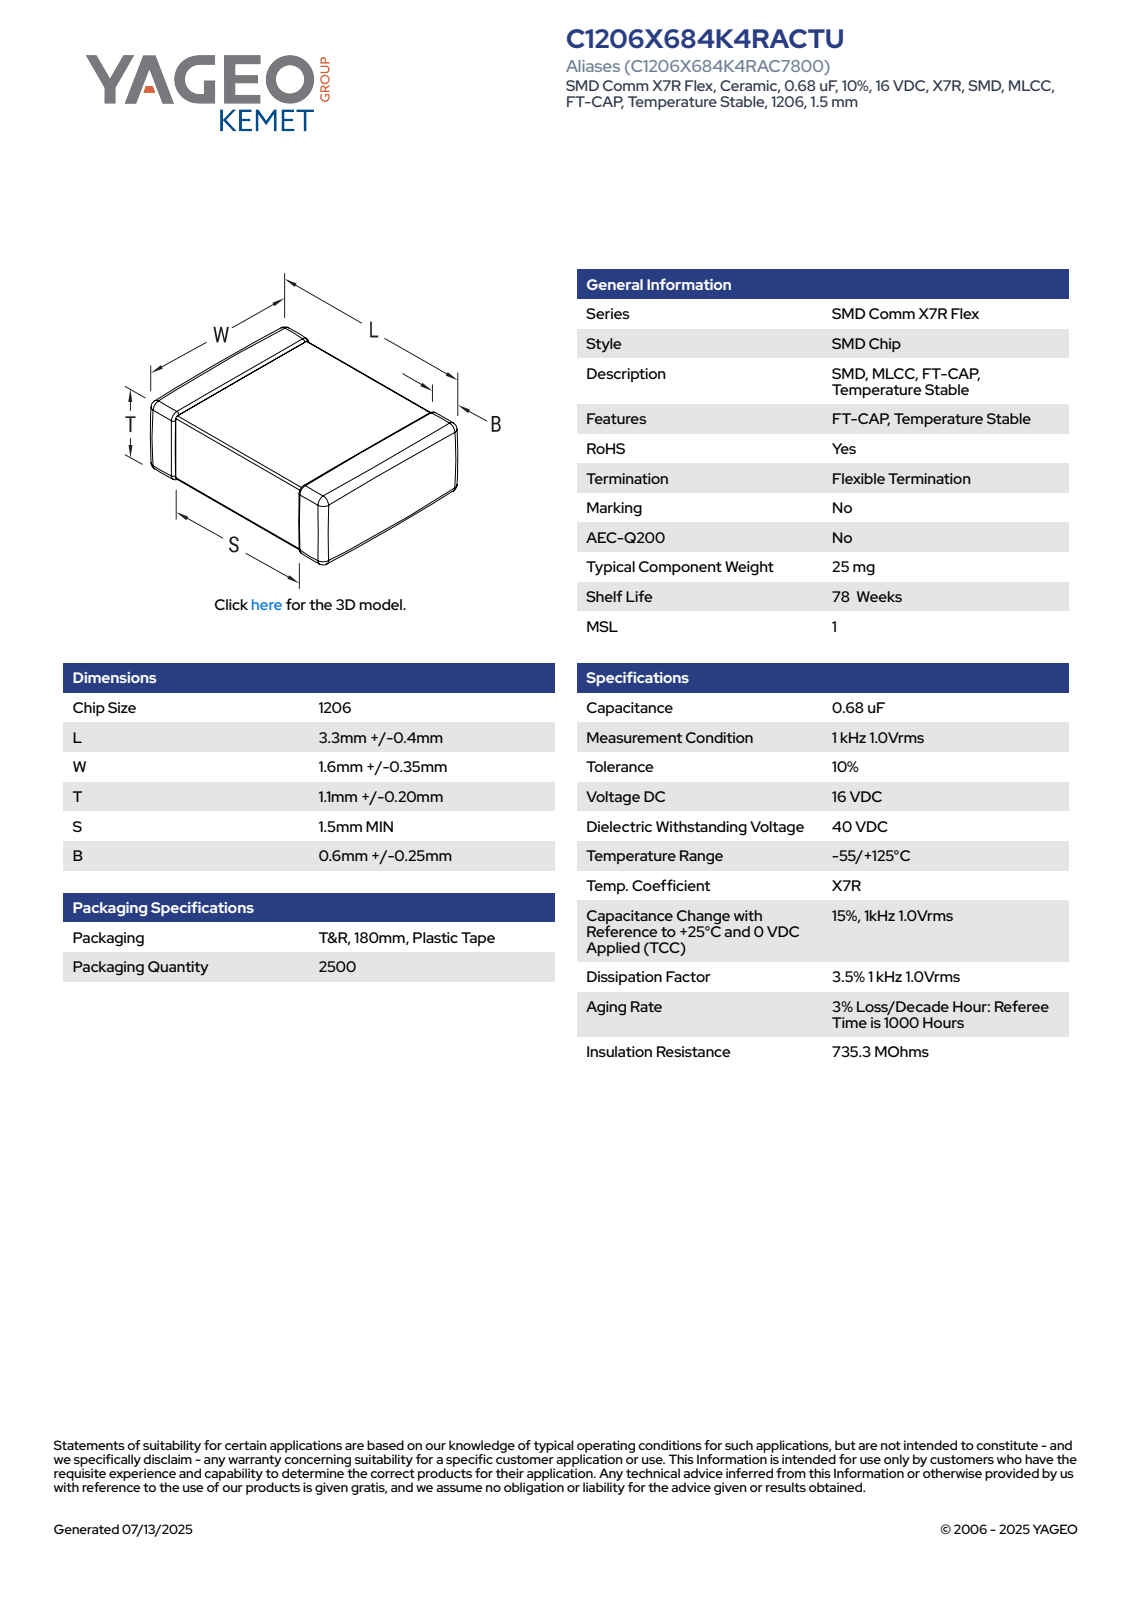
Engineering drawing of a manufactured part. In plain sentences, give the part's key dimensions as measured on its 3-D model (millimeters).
The part is named "CCS_CCSTD_1206_L3.7W1.95T1.3B0.6". Its 3-D file was written by "SolidWorks 2021 (AUTOMOTIVE_DESIGN)". It is 4 solids with 125 faces: 71 planar, 38 cylindrical and 16 other. Overall it measures 3.7 by 1.95 by 1.3 millimeters. Its volume is 9 cubic millimeters and its surface area 29 square millimeters. The main face-to-face distances are 1.26, 1.91, 1.22, 1.3, 3.7, 1.87, 1.95, 1.71, 1.99, 2.
